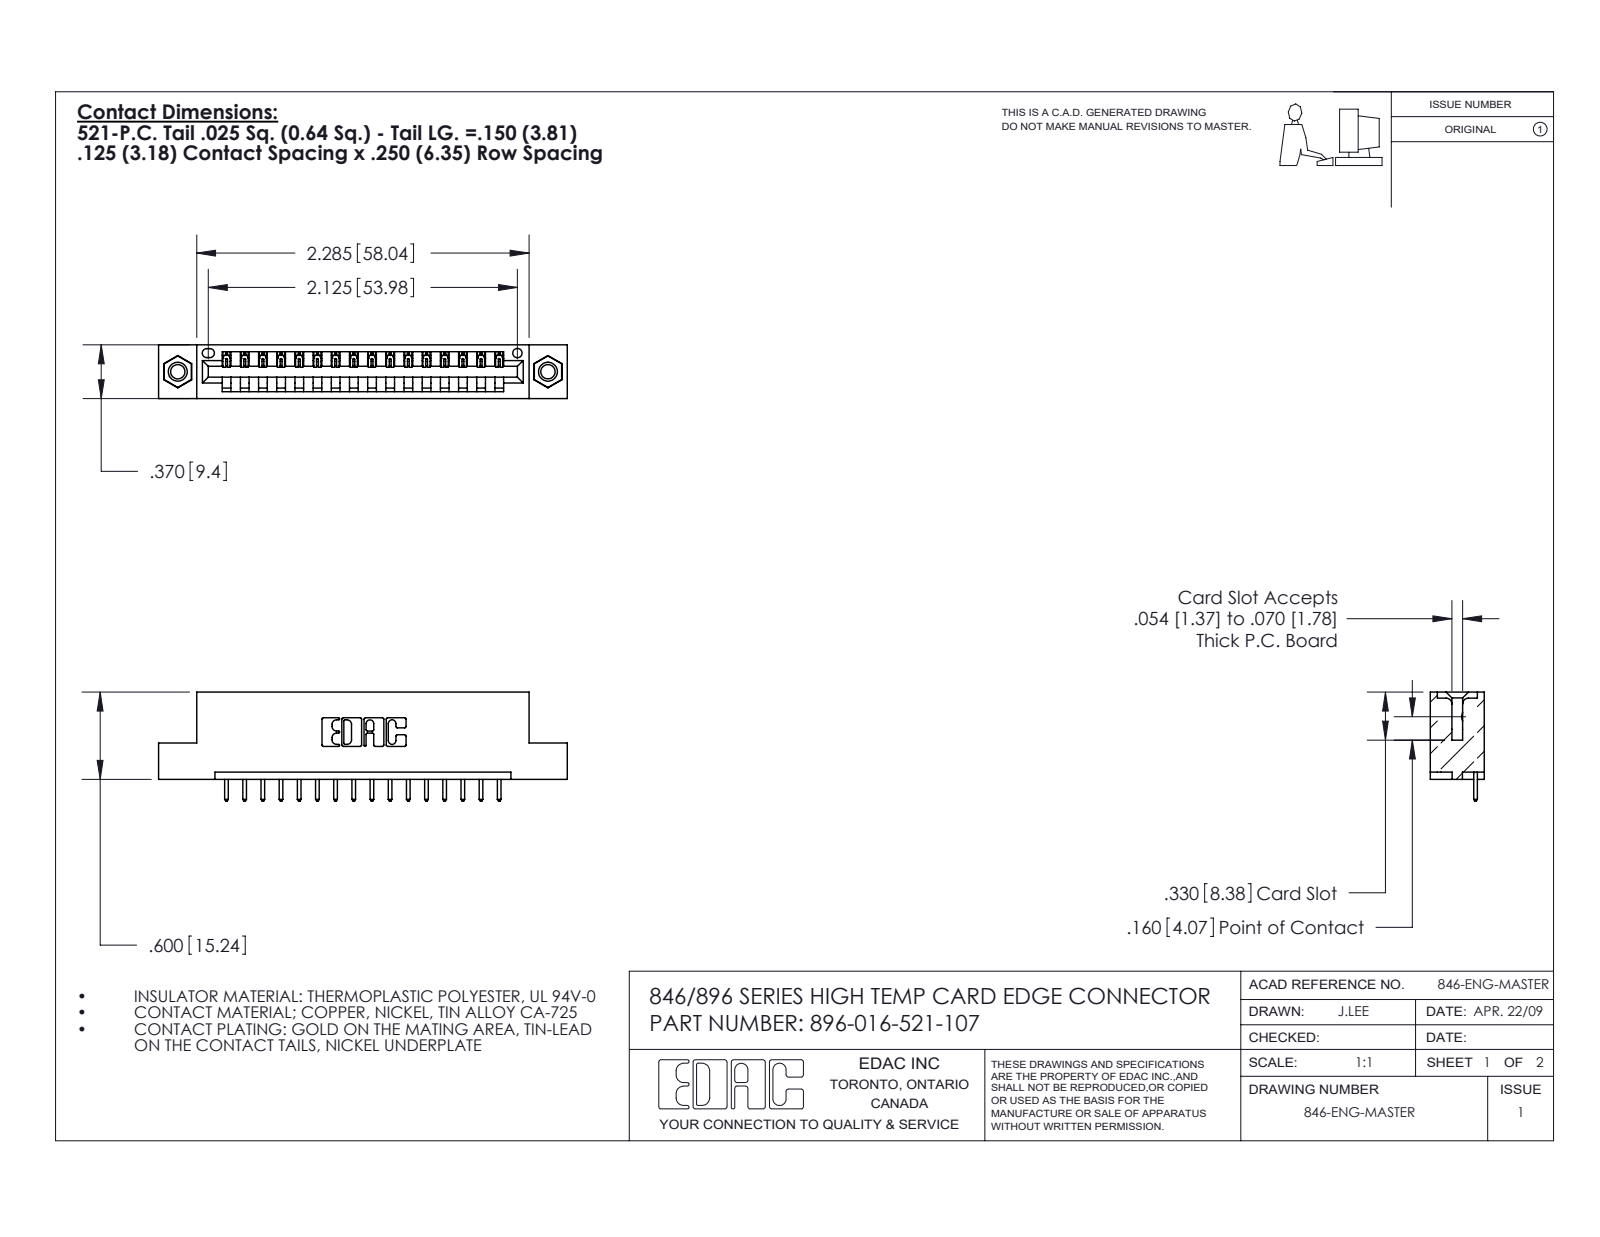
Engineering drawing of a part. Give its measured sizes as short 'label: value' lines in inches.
name: 345-292-001_345-293-121; 396-016-521-107; 345-250-001_345-250-005-103; 346 Part_Flush Mounting Lugs - 0.156 Dia-TI
written by: SolidWorks 2016 (CONFIG_CONTROL_DESIGN)
unit: in
bodies: 19 solids, 1110 faces (748 planar, 346 cylindrical, 16 other)
size: 2.81 × 0.75 × 0.37
volume: 0.402 in³; area: 12.11 in²
holes: 2× ⌀0.098, 2× ⌀0.125, 2× ⌀0.156, 1× ⌀0.064
bosses: 2× ⌀0.155
rounds: 32× R0.006, 32× R0.01, 22× R0.01, 6× R0.007, 6× R0.031, 3× R0.026, 2× R0.031, 2× R0.04
face distances: 0.048, 0.322, 0.25, 0.37, 0.072, 0.298, 0.025, 0.148, 0.222, 0.1
hole spacings: 0.246, 2.338, 2.545
